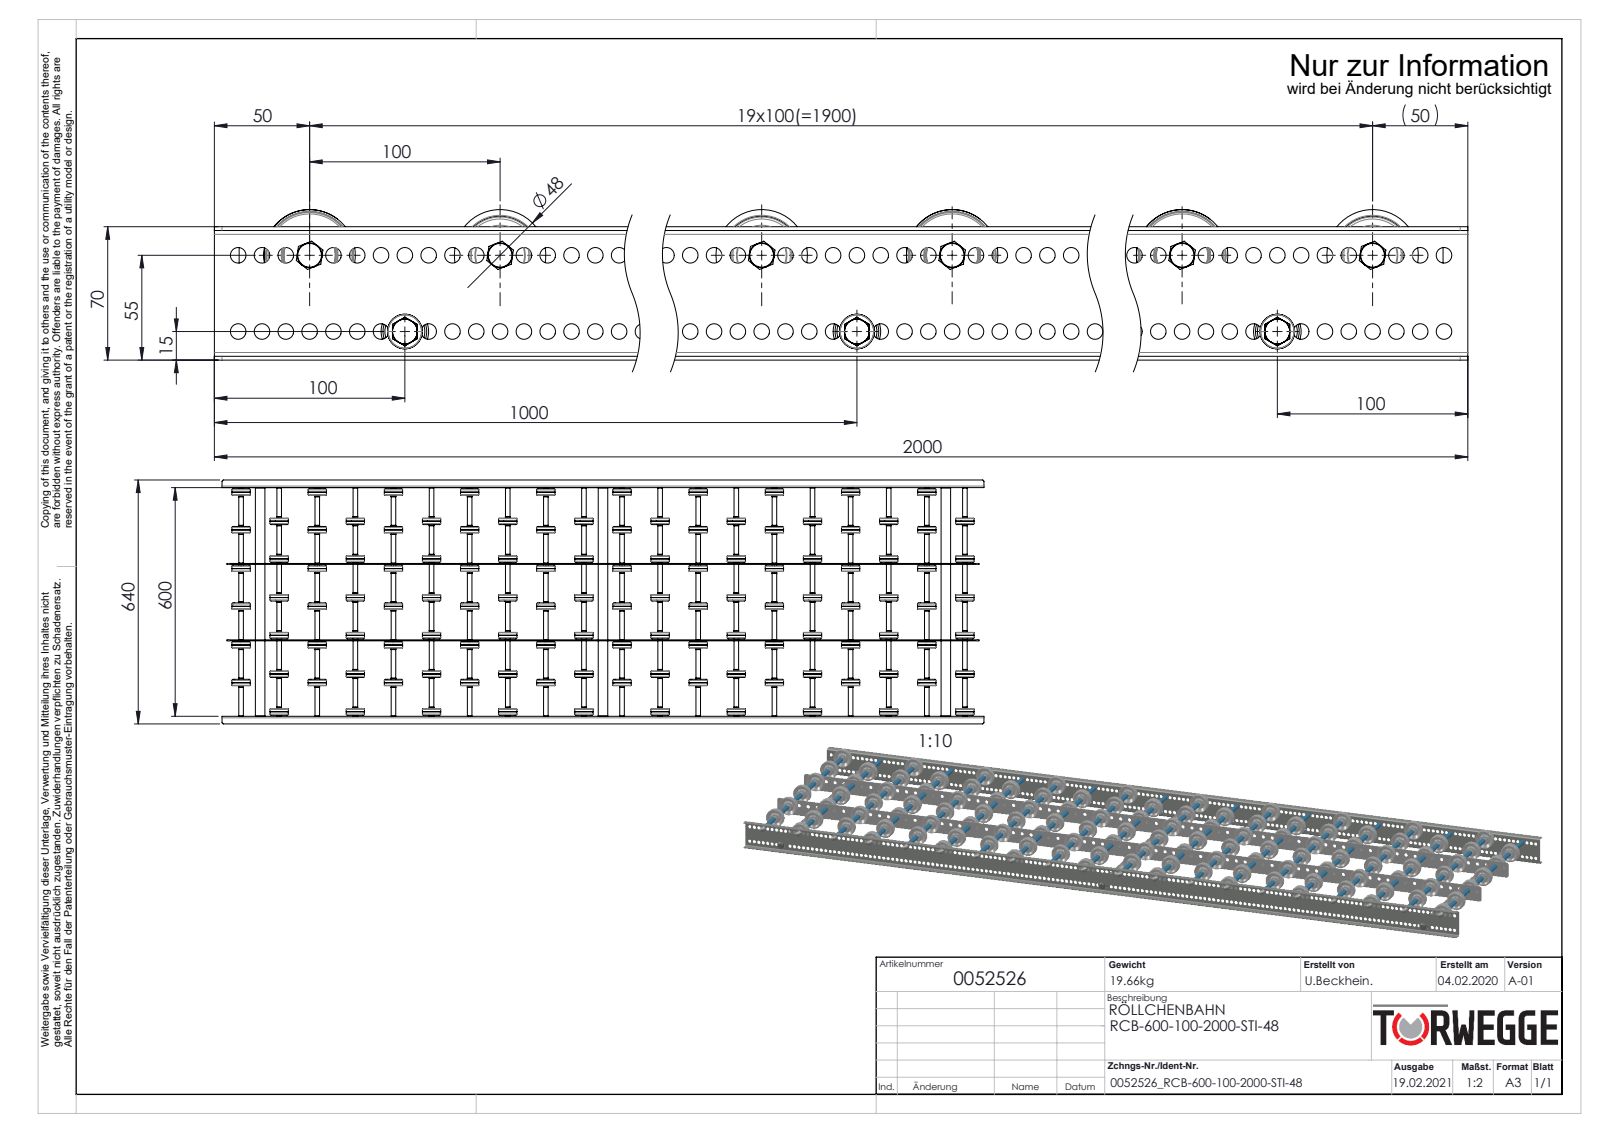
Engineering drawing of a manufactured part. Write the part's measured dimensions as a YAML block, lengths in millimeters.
part_name: "Hutmutter_DIN_1587_M8; 0052526; Profil_LRB-20x70x20x2_KFG_S100202_U-PROFIL-20-70-20-2-LRB-L=2000; K0011528_2200-48-8 (+6 more)"
step_written_by: "SolidWorks 2020 (AUTOMOTIVE_DESIGN)"
units: millimeters
bodies: {solids: 439, faces: 13602, planar: 2694, cylindrical: 5472, other: 5436}
overall_size: [2000, 640, 79]
volume: 4992000
surface_area: 3875000
round_holes:
  - {diameter: 8.2, count: 318}
  - {diameter: 8.5, count: 79}
  - {diameter: 6.65, count: 20}
  - {diameter: 8, count: 20}
  - {diameter: 9.65, count: 20}
  - {diameter: 15, count: 20}
  - {diameter: 41, count: 20}
  - {diameter: 6.8, count: 3}
  - {diameter: 21, count: 3}
round_bosses_or_shafts:
  - {diameter: 48, count: 20}
  - {diameter: 13, count: 20}
  - {diameter: 12.5, count: 20}
  - {diameter: 12.4, count: 20}
  - {diameter: 12, count: 20}
  - {diameter: 11.5, count: 20}
  - {diameter: 25, count: 3}
  - {diameter: 8, count: 3}
partial_cylinders:
  - {radius: 4, count: 8}
  - {radius: 2, count: 4}
  - {radius: 5, count: 4}
face_to_face_distances: [200.5, 2, 401, 602, 76, 99, 2.5, 198, 88, 111]
hole_center_spacings: [12.5, 25, 37.5, 50, 62.5, 75, 87.5, 100]
